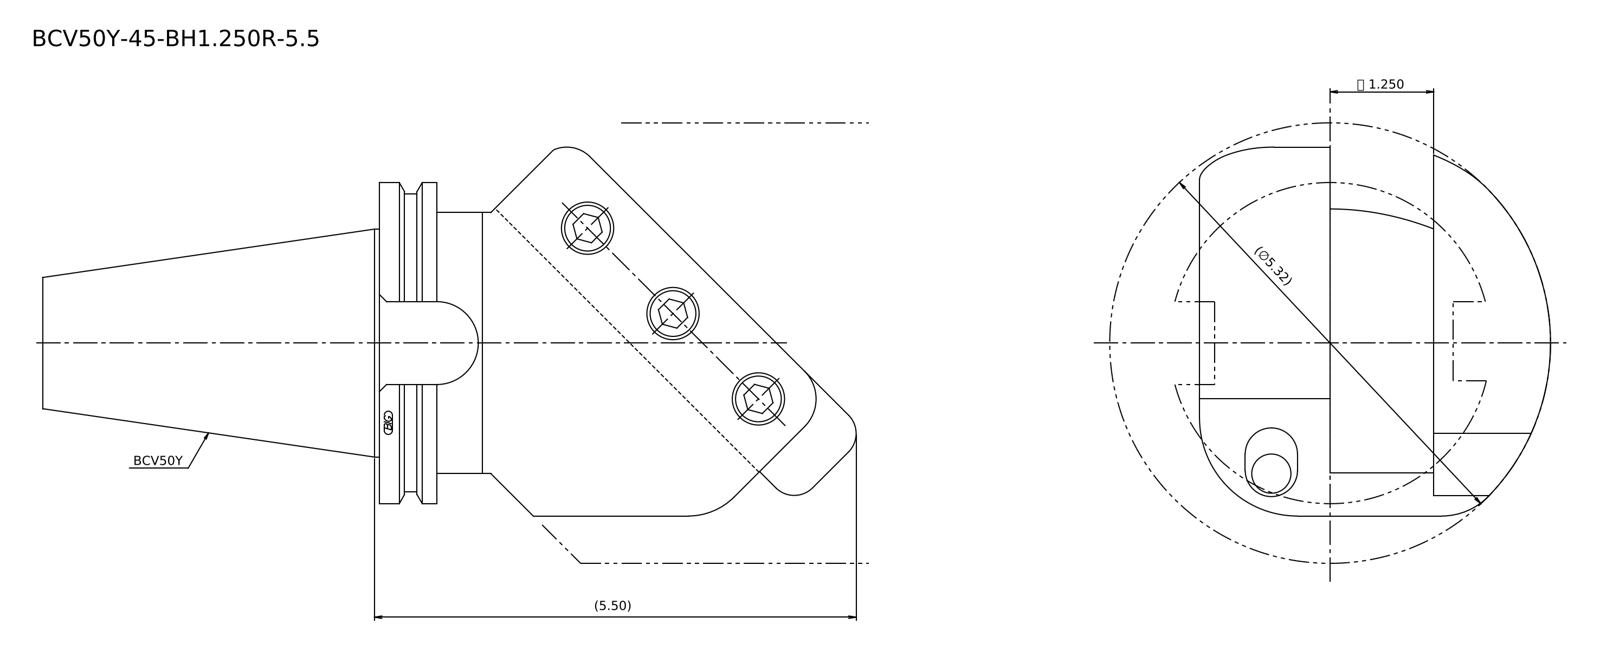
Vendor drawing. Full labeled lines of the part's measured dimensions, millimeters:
STEP written by: Kubotek KeyCreator 2011 V10.0.2 (22737) (automotive_design)
Units: millimetres
Bodies: 1 solid, 29 faces (15 planar, 10 cylindrical, 4 other)
Overall size (bounding box): 252.43 × 116.73 × 116.71
Volume: 1 097 000 mm³ · Surface area: 83 691 mm²
Round bosses / shafts (diameter × count): ⌀98.42 ×1, ⌀91.29 ×1, ⌀80 ×1, ⌀69.85 ×1
Partial cylindrical surfaces — rounded edges, fillets, slot ends (radius × count): R20 ×1, R30 ×1, R67.5 ×1
Main face-to-face distances: 71.75, 40, 31.75, 31.74, 17.55, 120.65, 103.1, 15, 31.49, 9.85
